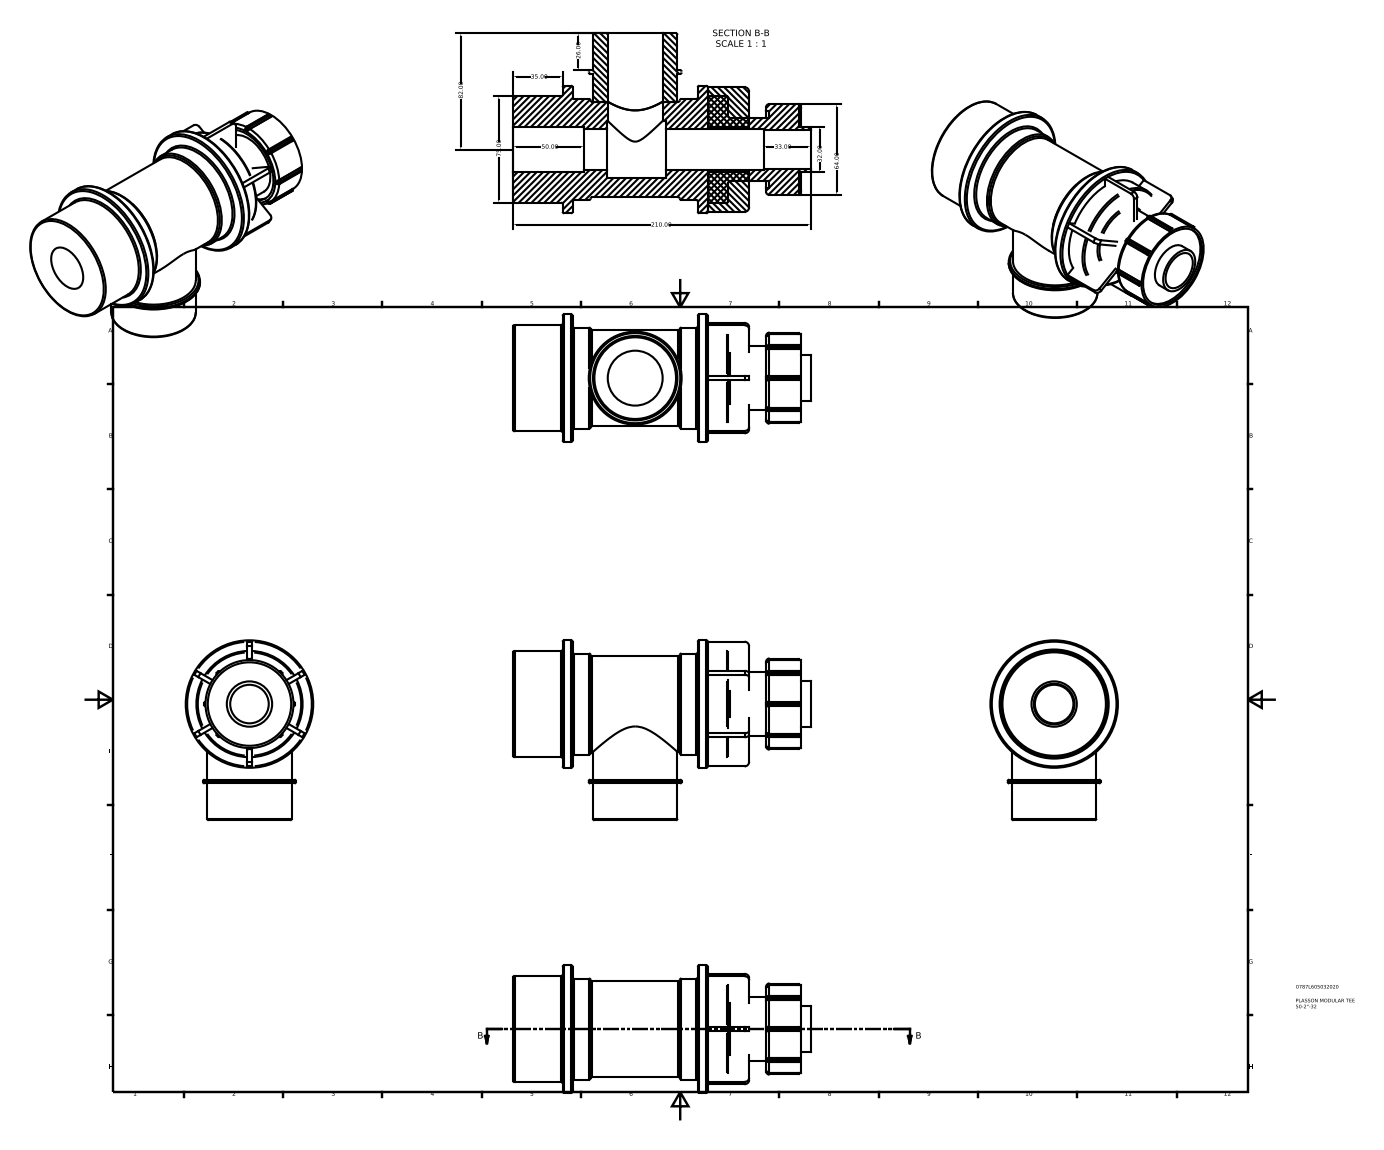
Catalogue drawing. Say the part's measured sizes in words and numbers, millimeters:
The part is named "0787L605032020". Its 3-D file was written by "Autodesk Inventor 2015 (AUTOMOTIVE_DESIGN)". It is 8 solids with 212 faces: 86 planar, 69 cylindrical and 57 other. Overall it measures 210 by 127 by 90 millimeters. Its volume is 670 991 cubic millimeters and its surface area 118 375 square millimeters. Round holes: 1 of diameter 27.2, 1 of diameter 28.8, 1 of diameter 32, 1 of diameter 38.75, 1 of diameter 40.32, 1 of diameter 54.4, 1 of diameter 58.88, 1 of diameter 67.5. Round bosses or shafts: 1 of diameter 90, 1 of diameter 75, 1 of diameter 71.25, 1 of diameter 65.58, 1 of diameter 62.08, 1 of diameter 59.61, 1 of diameter 45. Partial cylindrical surfaces (rounded edges, fillets, slot ends): 28 of radius 1, 8 of radius 2, 6 of radius 3.2. The main face-to-face distances are 3.2, 95.4, 7, 151.92, 137.4, 14.52, 201.75, 64.35, 49.83, 42.
